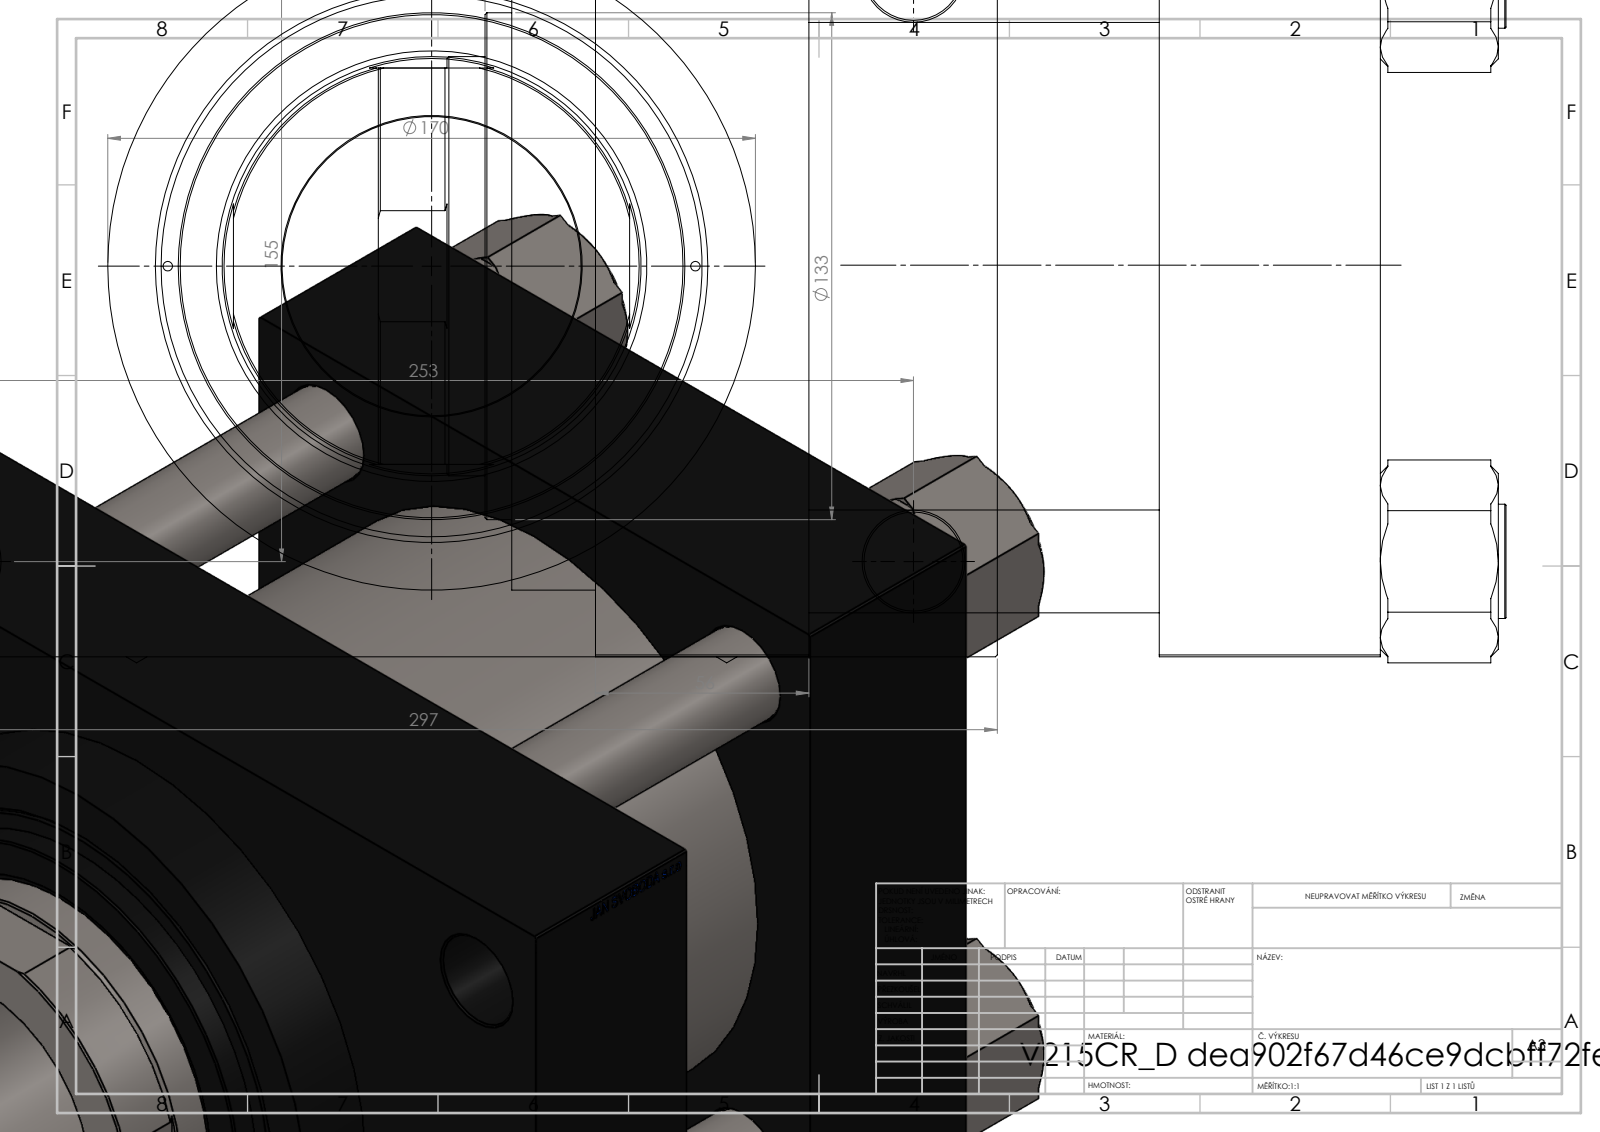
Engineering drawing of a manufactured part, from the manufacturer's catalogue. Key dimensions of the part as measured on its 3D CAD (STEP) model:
Part name (STEP PRODUCT): V215_VC_A; NUT_M5_D; V215CR_D_Body; V215CR_D_TYCINKA (+1 more)
STEP written by: SolidWorks 2019 (CONFIG_CONTROL_DESIGN)
Units: millimetres
Bodies: 11 solids, 1159 faces (547 planar, 92 cylindrical, 520 other)
Overall size (bounding box): 297 × 296 × 208.14
Volume: 8 127 000 mm³ · Surface area: 778 829 mm²
Round holes (diameter × count): ⌀26 ×4, ⌀27 ×4, ⌀2.5 ×2, ⌀7 ×2, ⌀33.24 ×2, ⌀45 ×2, ⌀78.5 ×1, ⌀110 ×1, ⌀113 ×1, ⌀120 ×1, ⌀142 ×1, ⌀160 ×1
Round bosses / shafts (diameter × count): ⌀30 ×4, ⌀170 ×1, ⌀166 ×1, ⌀133 ×1
Partial cylindrical surfaces — rounded edges, fillets, slot ends (radius × count): R54 ×1
Main face-to-face distances: 58, 150, 92, 205, 206, 148, 56, 46, 251, 72
Hole centre spacings: 49.05, 77.88, 96.35, 109.53, 148.35, 154.9, 162.53, 165.89
